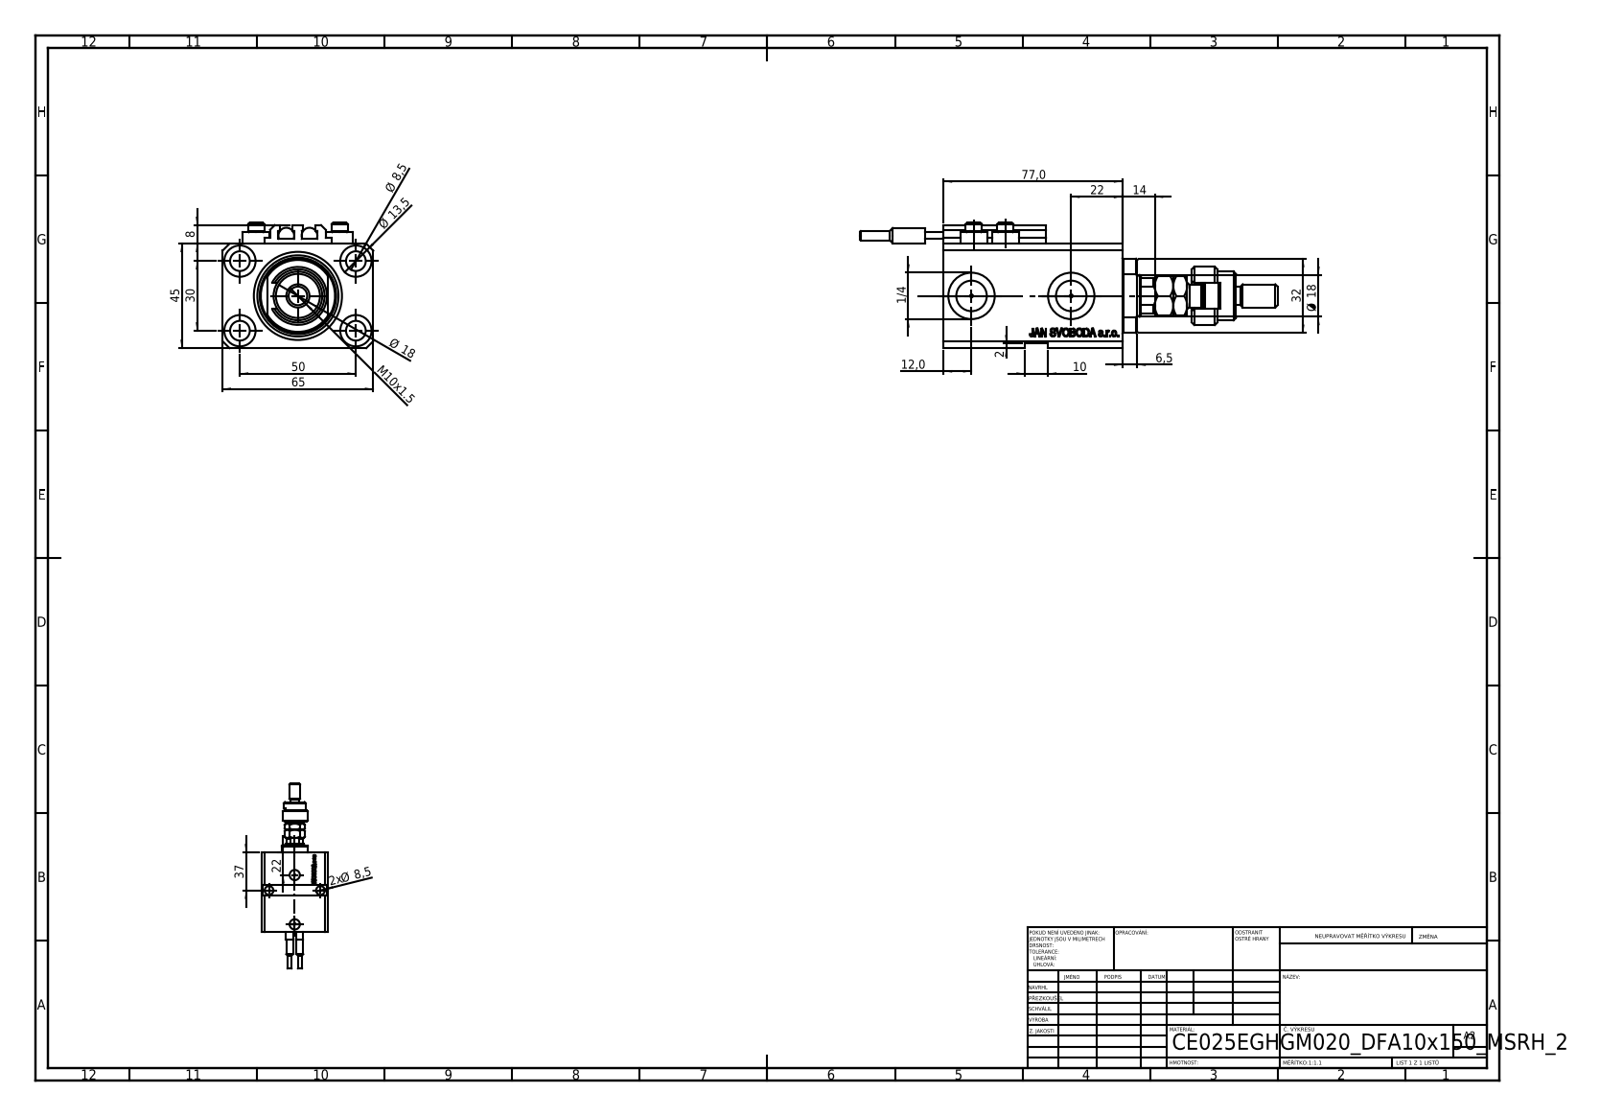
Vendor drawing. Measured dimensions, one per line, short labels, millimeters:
name: ALLEN BOLT V250CE; V250CE_E_Body; FEMALE_PART_FOR_DFA; MFA (+3 more)
written by: SolidWorks 2019 (CONFIG_CONTROL_DESIGN)
unit: mm
bodies: 12 solids, 1204 faces (571 planar, 151 cylindrical, 482 other)
size: 180 × 65 × 54
volume: 215 142 mm³; area: 67 381 mm²
holes: 7× ⌀8.5, 4× ⌀1.25, 4× ⌀4, 4× ⌀13.5, 2× ⌀10, 2× ⌀13.16, 2× ⌀20, 1× ⌀18, 1× ⌀38
bosses: 4× ⌀11.6, 4× ⌀7, 2× ⌀6.8, 2× ⌀6.5, 2× ⌀4, 1× ⌀25, 1× ⌀21, 1× ⌀16
rounds: 10× R0.2, 1× R5.5, 1× R8.5, 1× R8.75, 1× R16
face distances: 45, 14, 65, 63, 2, 77, 3, 5, 47, 6.9
hole spacings: 29.15, 50, 13.6, 15.12, 18.81, 18.97, 26.22, 26.61
